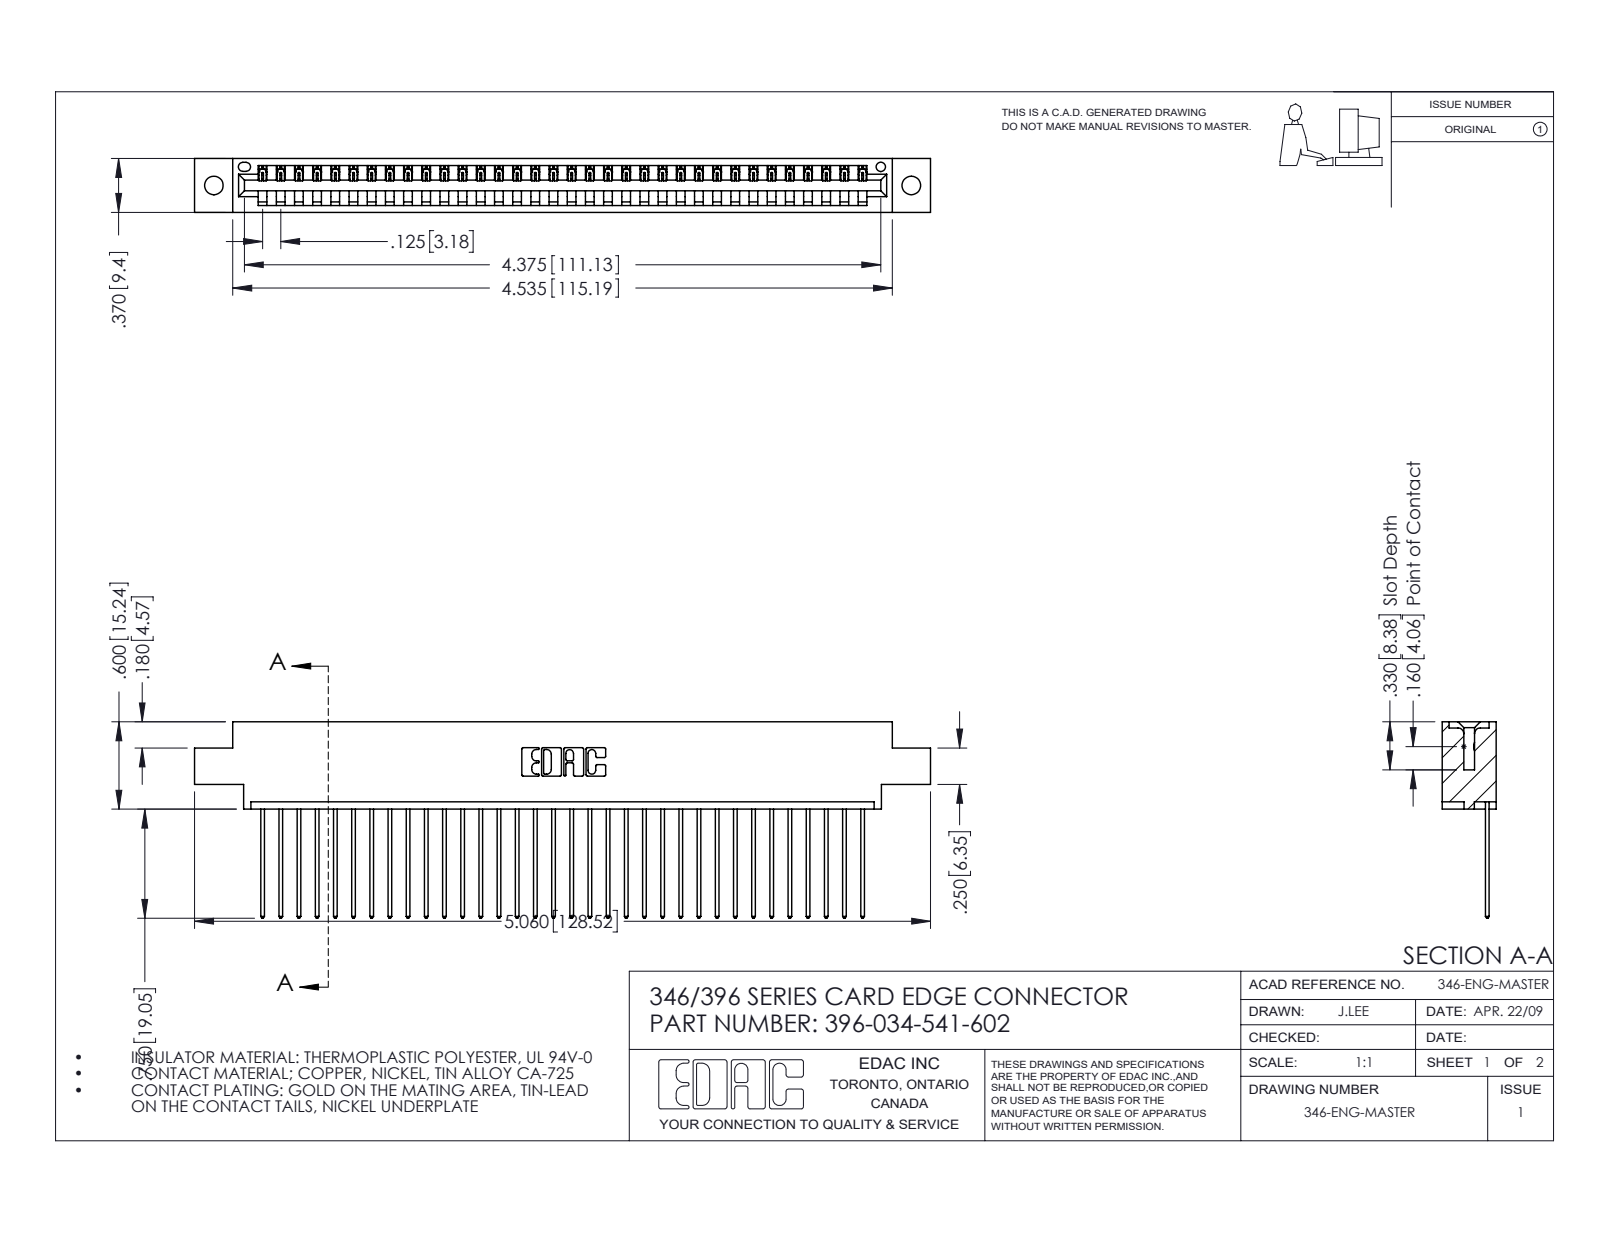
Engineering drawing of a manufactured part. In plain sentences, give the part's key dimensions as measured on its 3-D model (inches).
The part is named "346 Part_0.170 Offset - 0.128 Dia; 396-034-541-602; 345-292-001_345-293-141". Its 3-D file was written by "SolidWorks 2016 (CONFIG_CONTROL_DESIGN)". It is 35 solids with 2098 faces: 1440 planar, 658 cylindrical and 0 other. Overall it measures 5.06 by 1.35 by 0.37 inches. Its volume is 0.743 cubic inches and its surface area 24.31 square inches. Round holes: 2 of diameter 0.128, 1 of diameter 0.064. Partial cylindrical surfaces (rounded edges, fillets, slot ends): 68 of radius 0.006, 68 of radius 0.01, 22 of radius 0.01, 6 of radius 0.007, 6 of radius 0.031, 3 of radius 0.026, 2 of radius 0.031, 2 of radius 0.04. The main face-to-face distances are 0.048, 0.322, 0.37, 0.25, 0.072, 0.298, 0.025, 0.148, 0.222, 0.1. The hole center spacings are 0.246, 4.587, 4.795.
